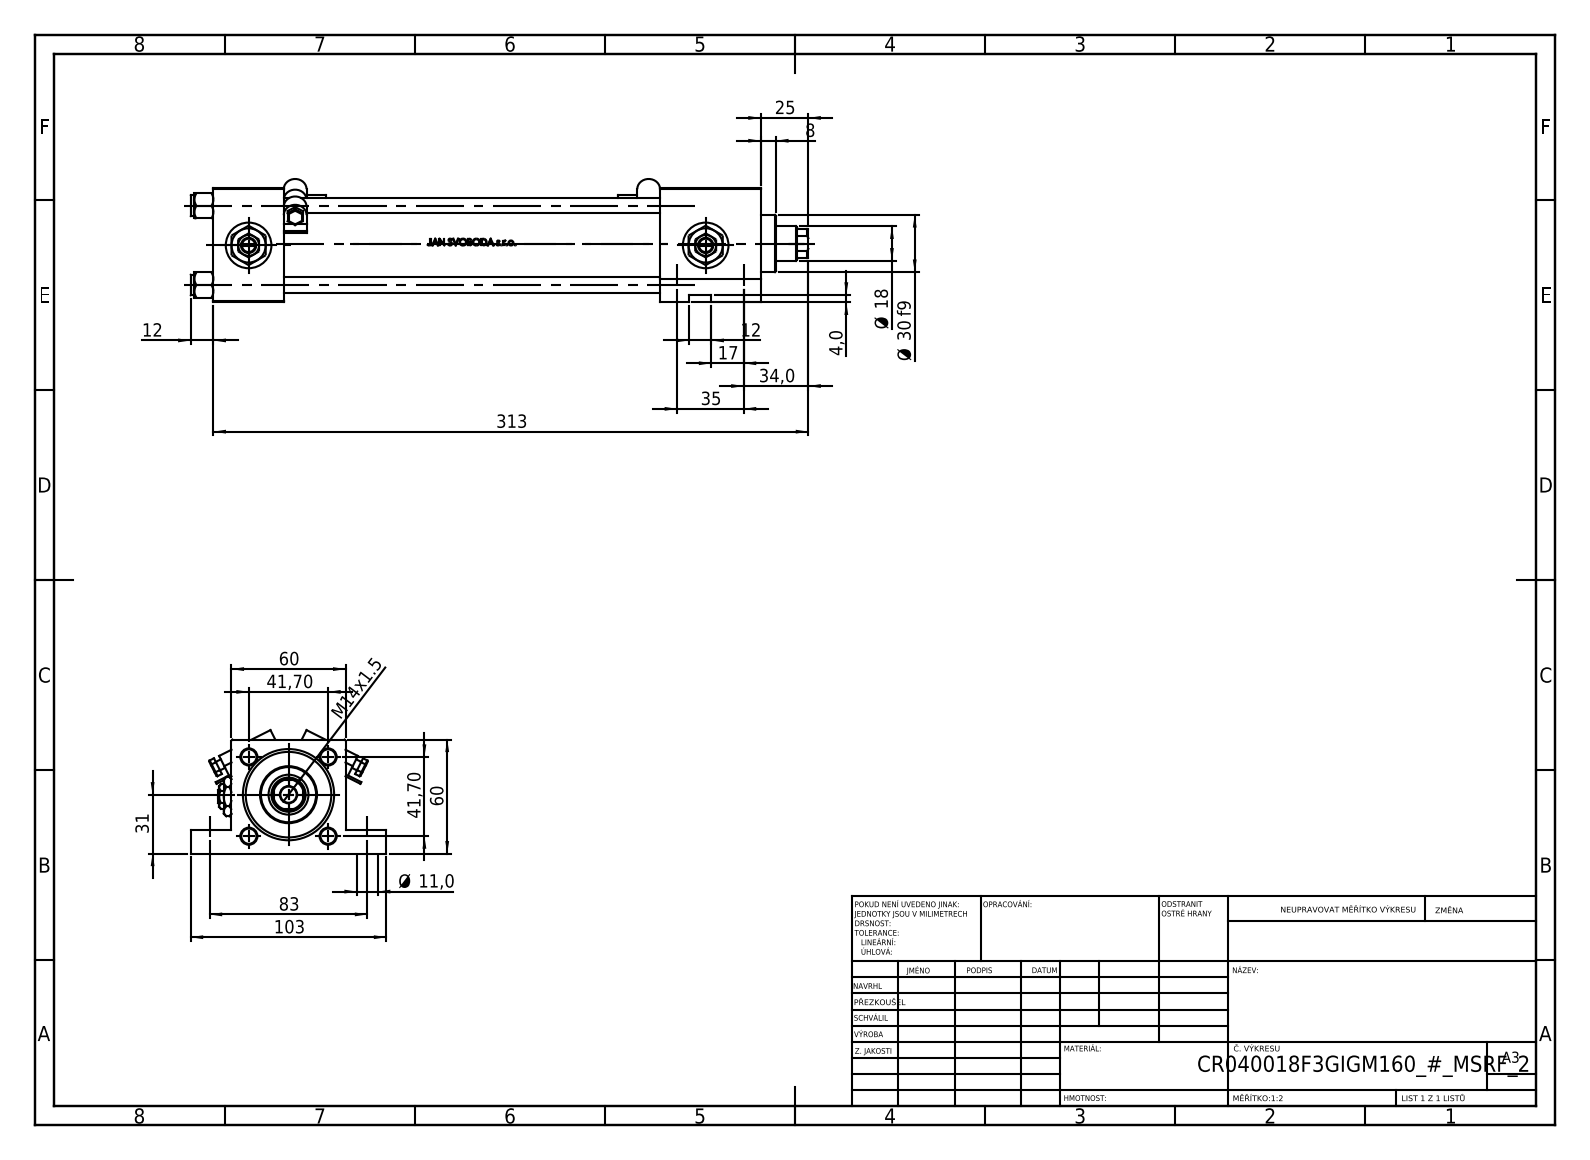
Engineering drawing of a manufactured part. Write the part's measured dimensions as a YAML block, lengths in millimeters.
part_name: "V215_VC_A; Zatka_pro_OIL_PORT; NUT_M5_F; V215CR_F_TYCINKA (+3 more)"
step_written_by: "SolidWorks 2019 (CONFIG_CONTROL_DESIGN)"
units: millimeters
bodies: {solids: 15, faces: 1279, planar: 520, cylindrical: 177, other: 582}
overall_size: [325, 103, 64.97]
volume: 547959
surface_area: 178578
round_holes:
  - {diameter: 8, count: 4}
  - {diameter: 11, count: 4}
  - {diameter: 16.66, count: 3}
  - {diameter: 24, count: 3}
  - {diameter: 7, count: 2}
  - {diameter: 8.5, count: 1}
  - {diameter: 16, count: 1}
  - {diameter: 18, count: 1}
  - {diameter: 21, count: 1}
  - {diameter: 31, count: 1}
  - {diameter: 40, count: 1}
  - {diameter: 45, count: 1}
round_bosses_or_shafts:
  - {diameter: 11, count: 4}
  - {diameter: 5, count: 2}
  - {diameter: 2.5, count: 2}
  - {diameter: 46, count: 1}
  - {diameter: 30, count: 1}
partial_cylinders:
  - {radius: 0.5, count: 12}
  - {radius: 6, count: 4}
  - {radius: 8.5, count: 1}
face_to_face_distances: [60, 37, 288, 235, 53, 251, 198, 259.3, 222.3, 24.3]
hole_center_spacings: [41.7, 28.79, 30.2, 35, 42.09, 50.06, 58.97, 83]
